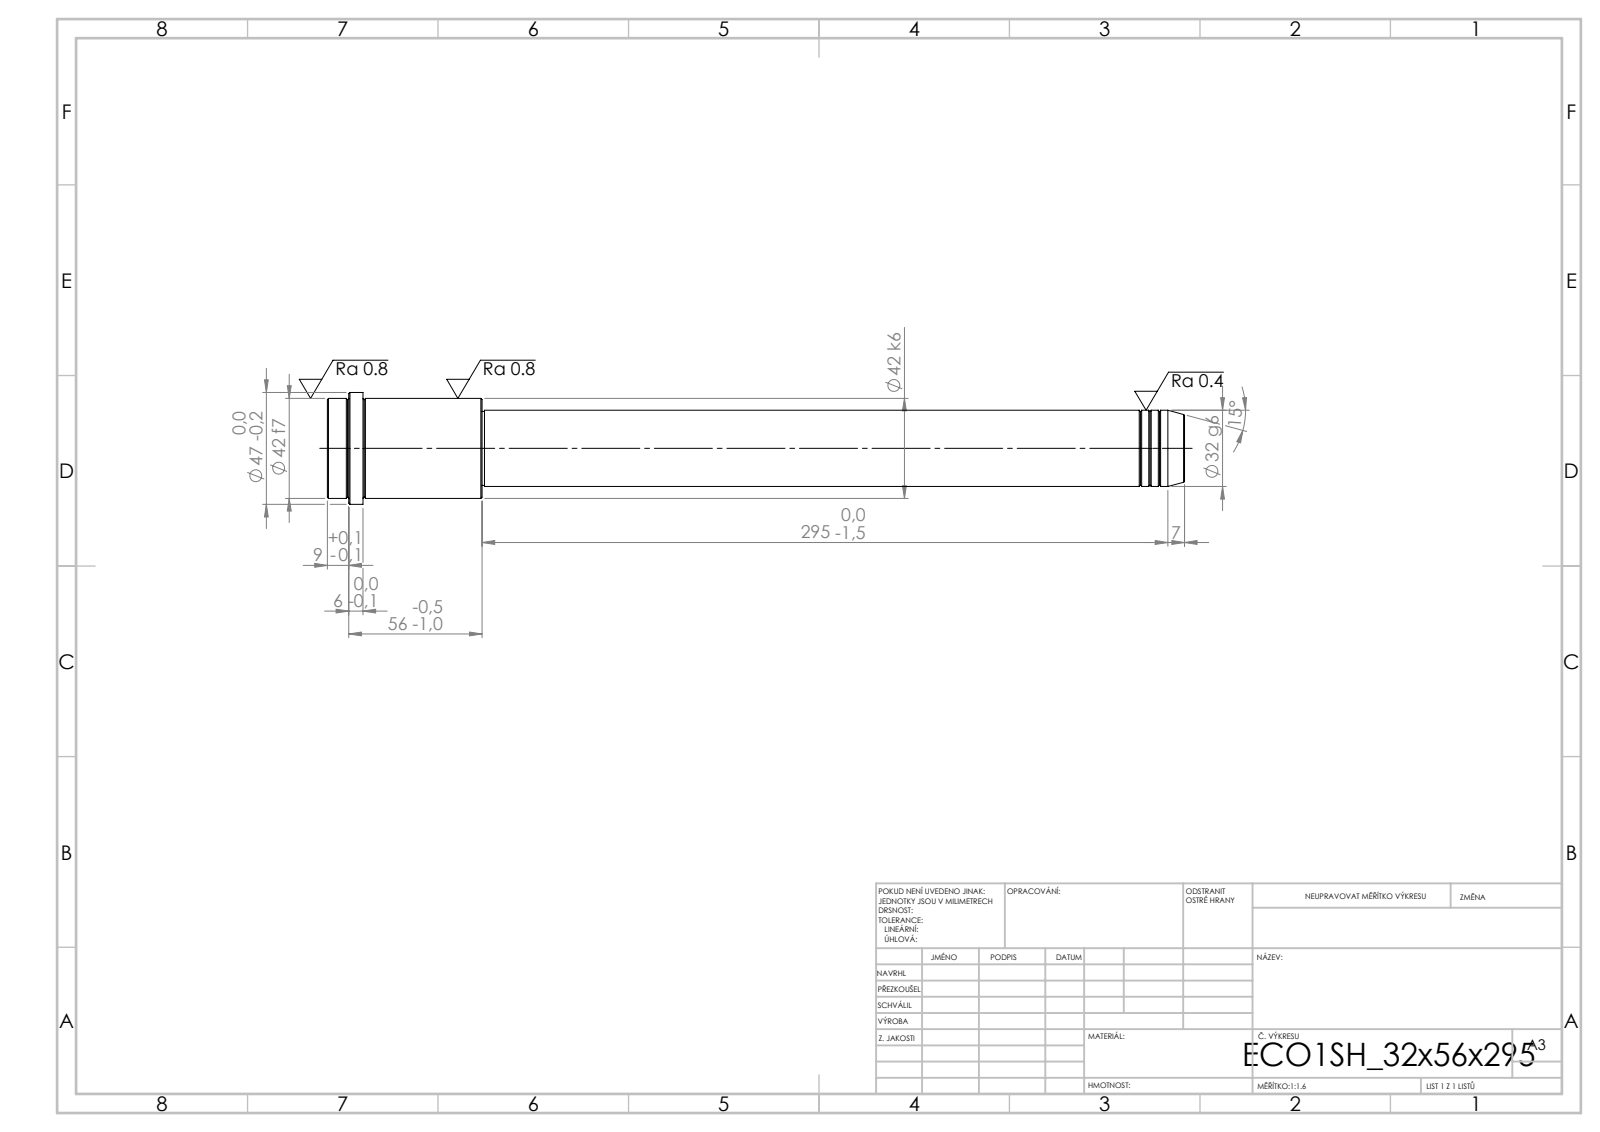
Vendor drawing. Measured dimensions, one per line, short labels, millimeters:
written by: SolidWorks 2019 (CONFIG_CONTROL_DESIGN)
unit: mm
bodies: 1 solid, 52 faces (6 planar, 16 cylindrical, 30 other)
size: 360 × 47 × 47
volume: 328 447 mm³; area: 41 873 mm²
bosses: 1× ⌀47, 1× ⌀42, 1× ⌀32, 1× ⌀31
face distances: 360, 295, 65, 345, 50, 15, 351, 56, 6, 9
